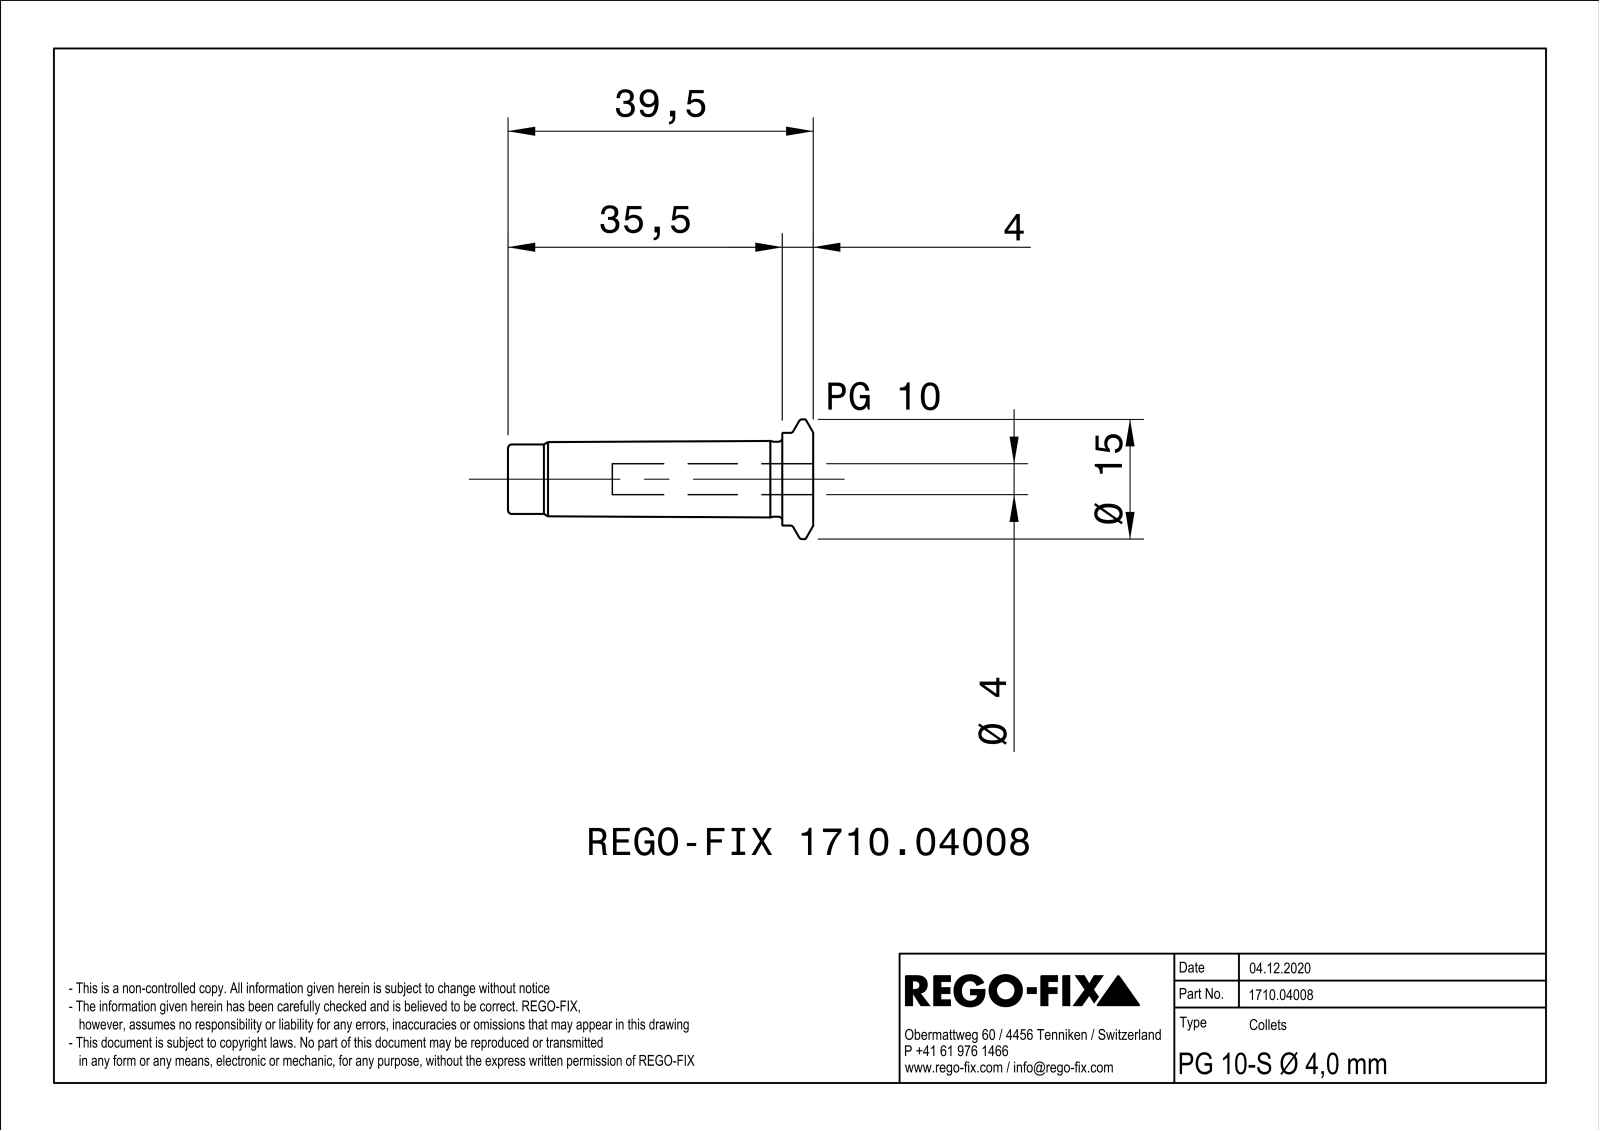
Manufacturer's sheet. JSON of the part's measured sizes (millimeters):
{"part_name": "NOCUT", "step_written_by": "SIEMENS PLM Software Solid Edge ST10 (AUTOMOTIVE_DESIGN)", "units": "millimeters", "bodies": {"solids": 0, "faces": 61, "planar": 11, "cylindrical": 18, "other": 32}, "overall_size": [39.5, 15.5, 15.49], "round_holes": [[4, 1], [6.19, 1]], "round_bosses_or_shafts": [[15.5, 1], [12, 1], [9.7, 1], [9, 1]], "partial_cylinders_radius": [[0.4, 6]], "face_to_face_distances": [0.8, 39.5, 4, 35.5]}
